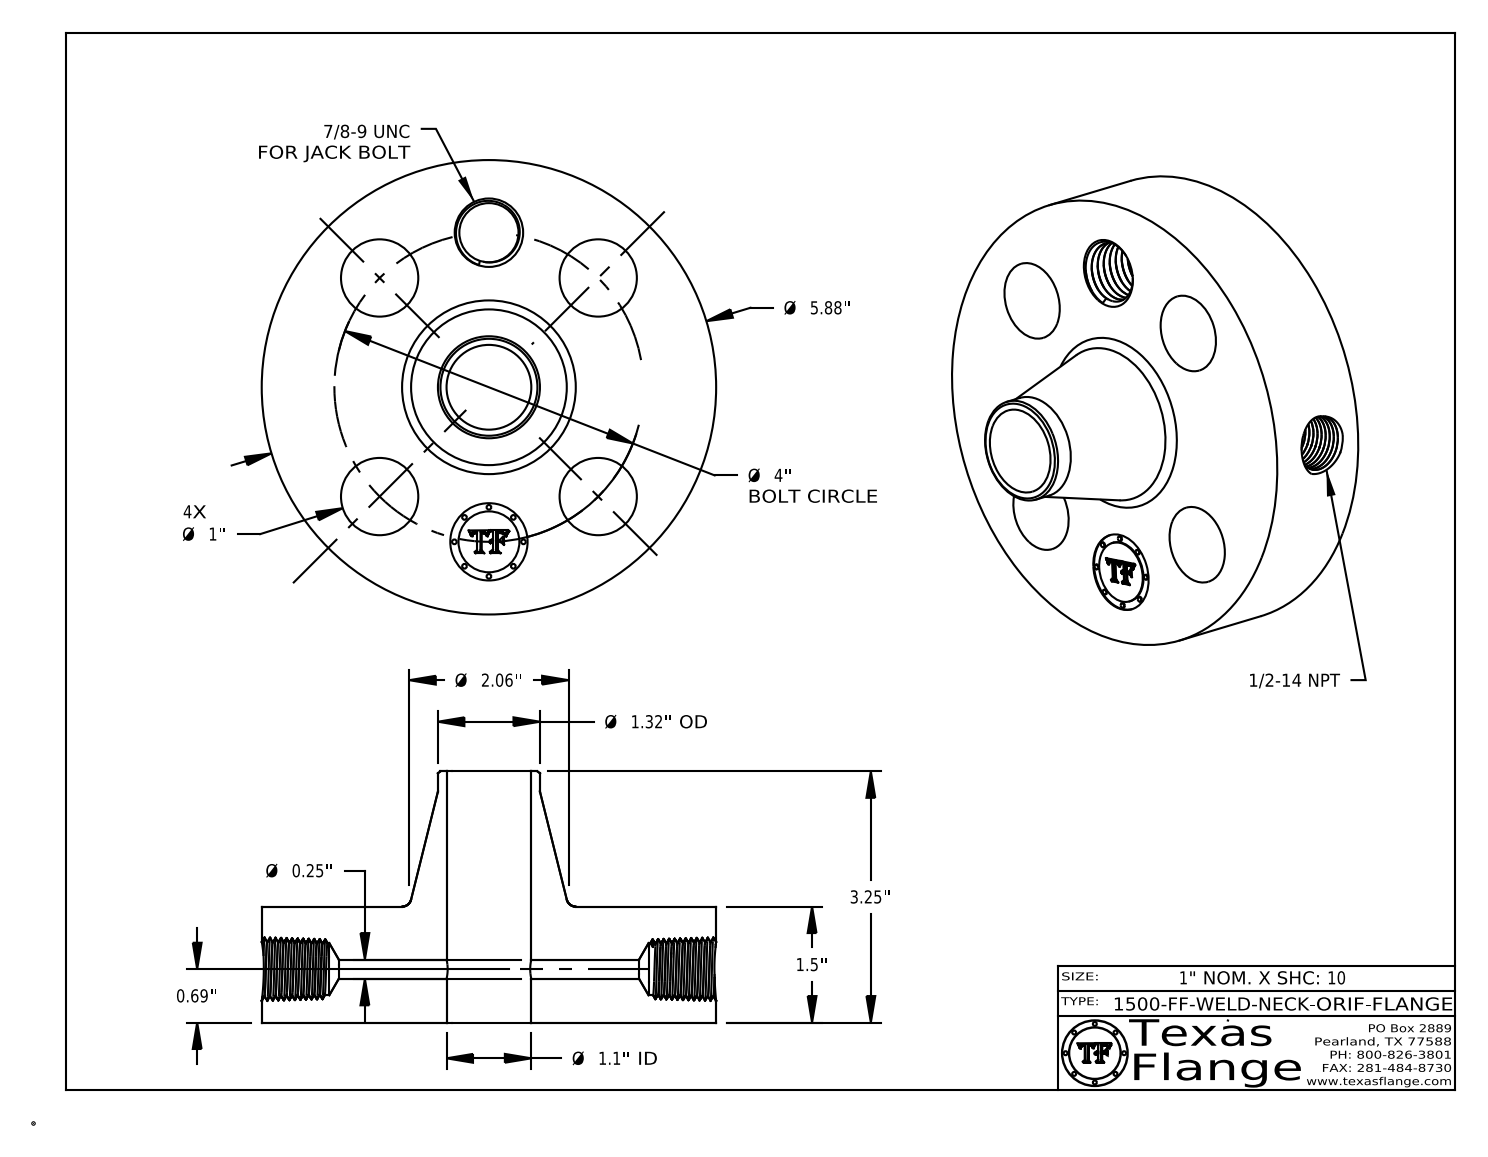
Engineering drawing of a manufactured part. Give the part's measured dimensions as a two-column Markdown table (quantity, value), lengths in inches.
| quantity | value |
| --- | --- |
| part name | 1500-FF-WELD-NECK |
| STEP written by | CATIA V5 STEP AP214 (AUTOMOTIVE_DESIGN) |
| units | inches |
| bodies | 1 solid, 746 faces (368 planar, 80 cylindrical, 298 other) |
| overall size | 5.88 × 5.88 × 3.25 |
| volume | 34.99 in³ |
| surface area | 124.4 in² |
| round holes (diameter × count) | 1 × 5, 0.25 × 1, 0.672 × 1, 0.766 × 1, 1.097 × 1 |
| round bosses / shafts (diameter × count) | 0.061 × 8, 5.88 × 1, 1.32 × 1, 0.788 × 1 |
| main face-to-face distances | 1.5, 1.485, 0.015, 3.25, 1.765, 1.75, 0.298, 0.293, 0.054, 0.248 |
| hole center spacings | 2, 1.531, 2.828, 3.695, 4 |
